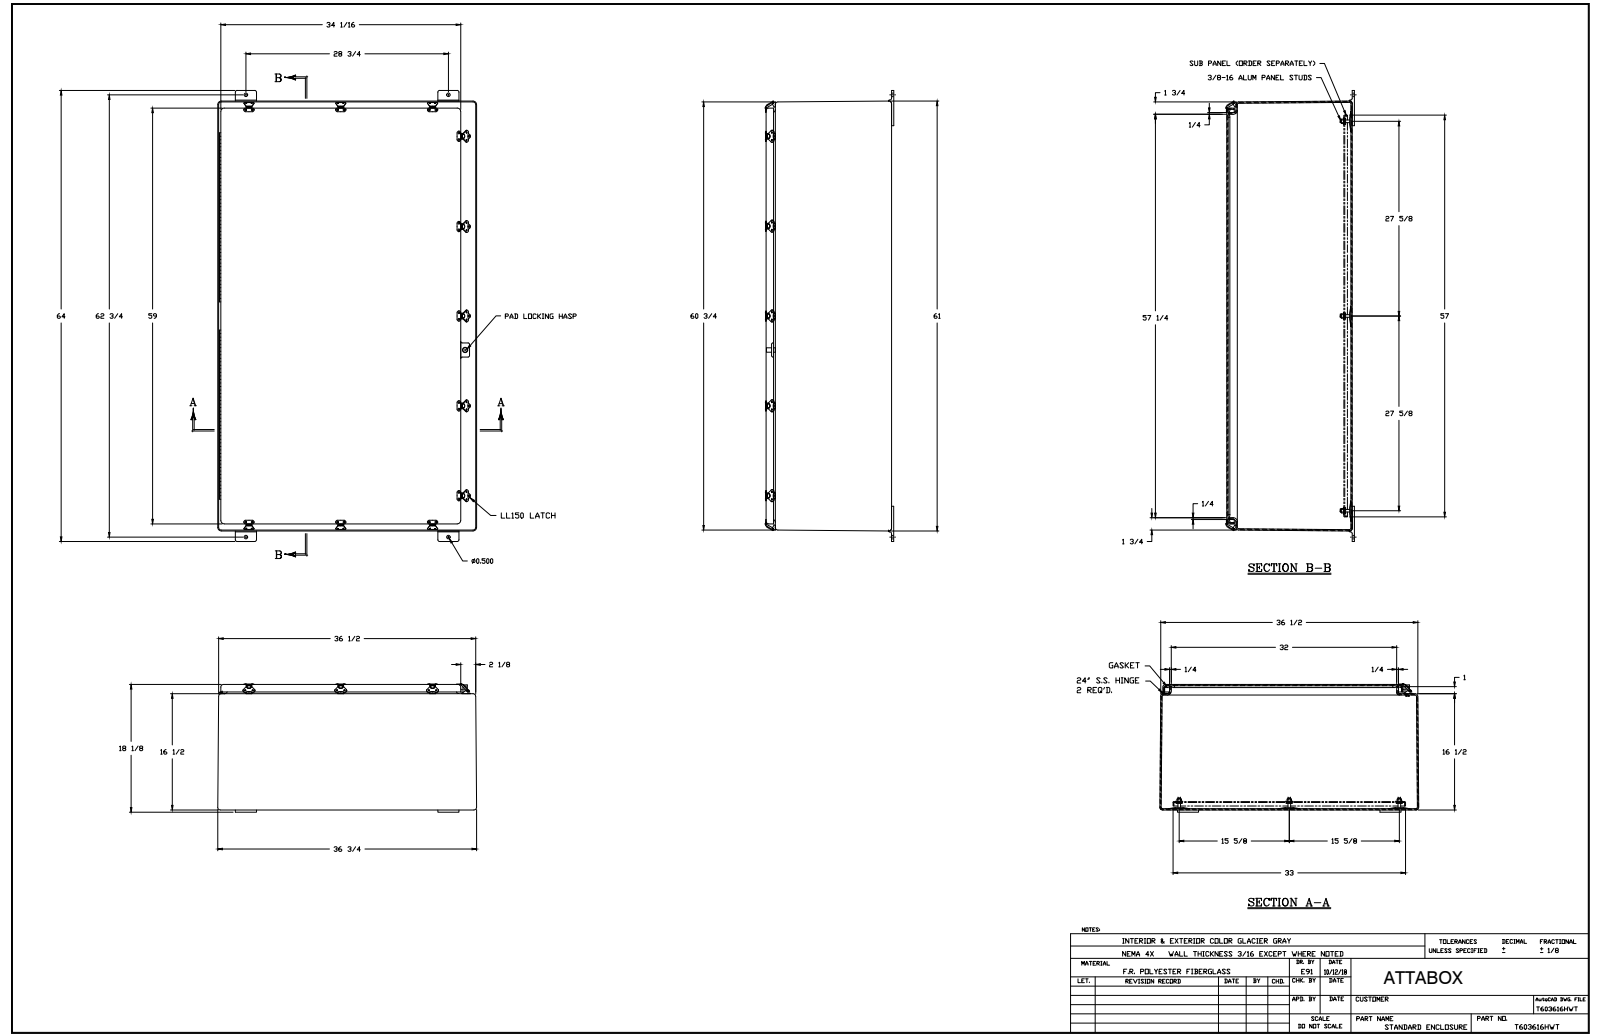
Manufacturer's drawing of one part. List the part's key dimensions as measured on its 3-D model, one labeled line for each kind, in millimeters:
Part name (STEP PRODUCT): T603616HWT
STEP written by: SolidWorks 2018 (AUTOMOTIVE_DESIGN)
Units: millimetres
Bodies: 127 solids, 3132 faces (1212 planar, 1300 cylindrical, 620 other)
Overall size (bounding box): 1625.6 × 933.5 × 466.5
Volume: 23 810 000 mm³ · Surface area: 10 990 000 mm²
Round holes (diameter × count): ⌀3.3 ×74, ⌀1.6 ×44, ⌀3.5 ×22, ⌀4.7 ×22, ⌀1.7 ×12, ⌀9.5 ×6, ⌀1.7 ×4, ⌀12.7 ×4, ⌀3.4 ×3, ⌀4 ×3, ⌀9.5 ×2, ⌀3.2 ×1
Round bosses / shafts (diameter × count): ⌀3.6 ×44, ⌀7.5 ×16, ⌀12.7 ×11, ⌀5.1 ×3, ⌀6.4 ×1, ⌀5.1 ×1, ⌀3.4 ×1
Partial cylindrical surfaces — rounded edges, fillets, slot ends (radius × count): R0.3 ×243, R0.8 ×44, R7.9 ×39, R9.5 ×23, R5.3 ×22, R30.1 ×22, R6.4 ×18, R1 ×14
Main face-to-face distances: 4.7, 3.2, 452.5, 449.2, 4.8, 447.6, 444.5, 928.7, 1544.7, 933.5
Hole centre spacings: 190.5, 393.7, 323.9, 711.2, 331, 647.7, 25.4, 203.2
